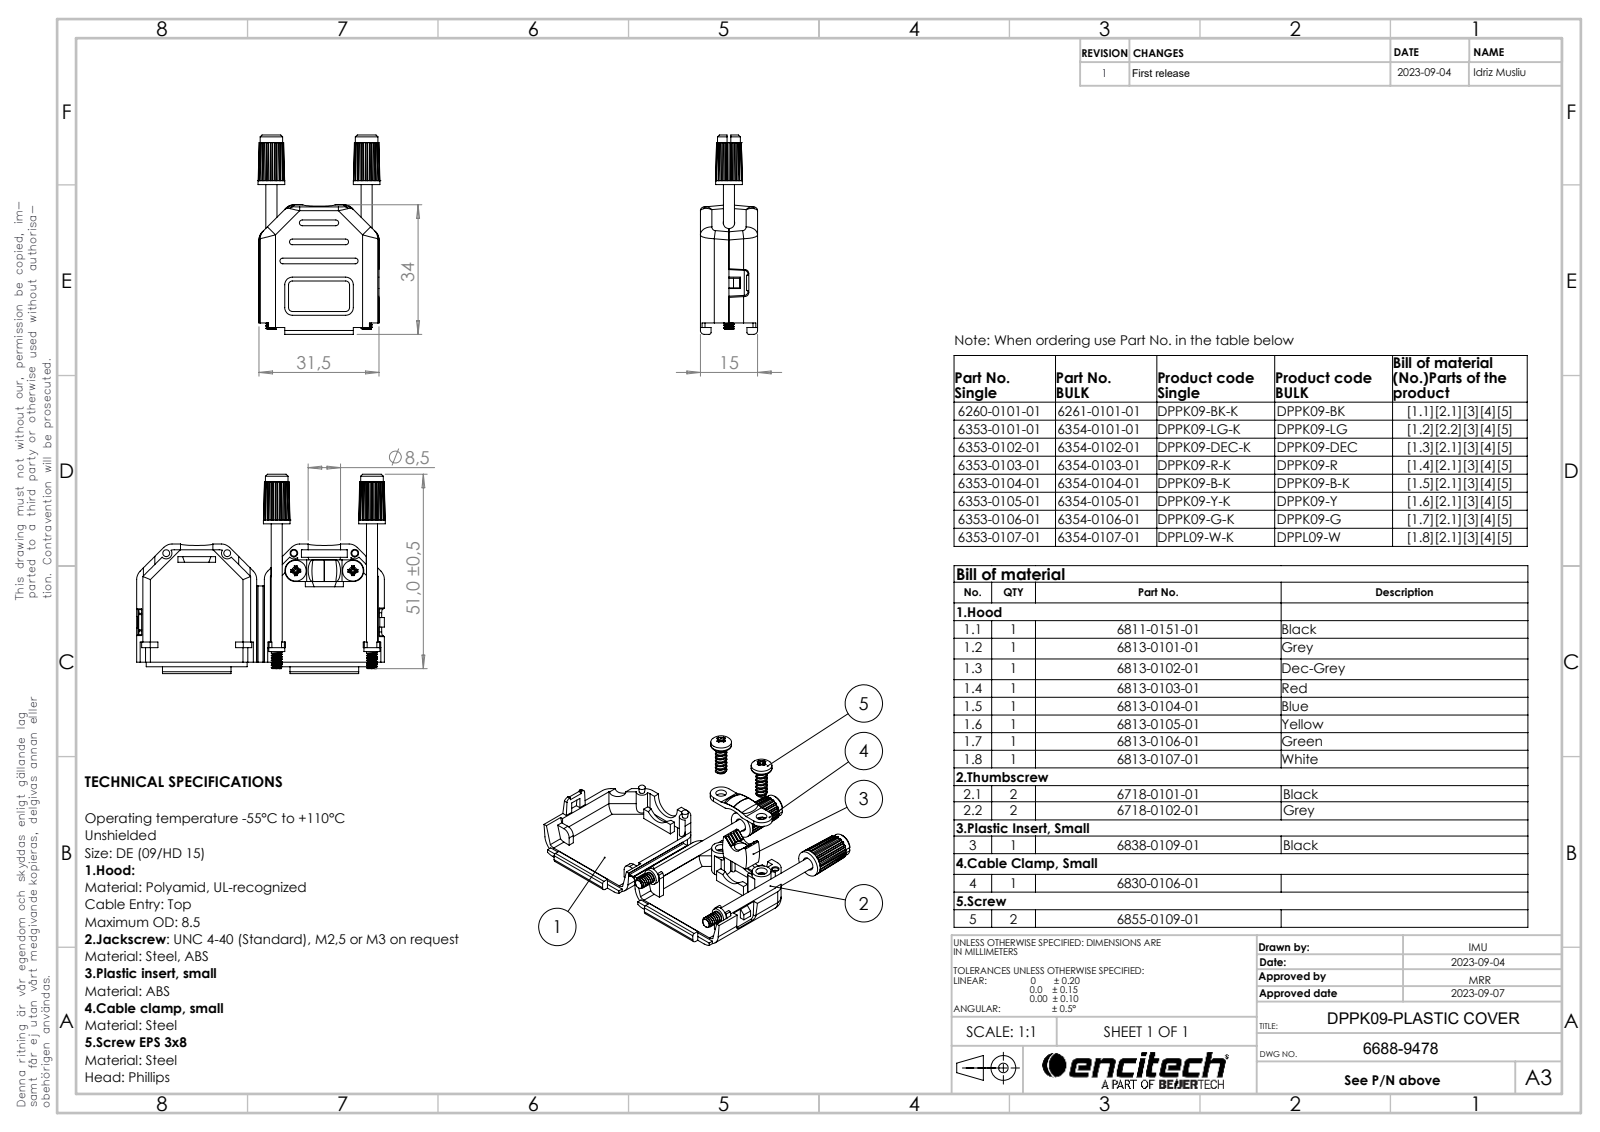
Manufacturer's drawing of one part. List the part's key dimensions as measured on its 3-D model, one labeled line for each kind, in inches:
Part name (STEP PRODUCT): 6830-0106-01; 6718-0101-01; 6811-0151-01 Part 1; 6855-0109-01 (+3 more)
STEP written by: SolidWorks 2023 (AUTOMOTIVE_DESIGN)
Units: inches
Bodies: 10 solids, 839 faces (481 planar, 240 cylindrical, 118 other)
Overall size (bounding box): 2.059 × 1.26 × 0.591
Volume: 0.392 in³ · Surface area: 14.48 in²
Round holes (diameter × count): ⌀0.118 ×4, ⌀0.063 ×2, ⌀0.079 ×2, ⌀0.094 ×2, ⌀0.11 ×2, ⌀0.138 ×1, ⌀0.335 ×1
Round bosses / shafts (diameter × count): ⌀0.276 ×2, ⌀0.236 ×2, ⌀0.215 ×2, ⌀0.197 ×2, ⌀0.165 ×2, ⌀0.114 ×2, ⌀0.112 ×2, ⌀0.097 ×2
Partial cylindrical surfaces — rounded edges, fillets, slot ends (radius × count): R0.079 ×15, R0.118 ×14, R0.039 ×12, R0.02 ×10, R0.03 ×6, R0.016 ×4, R0.157 ×4, R0.059 ×2
Main face-to-face distances: 0.067, 0.524, 0.457, 0.591, 0.228, 0.295, 0.063, 0.059, 0.583, 0.047
Hole centre spacings: 0.182, 0.295, 0.365, 0.492, 0.637, 0.591, 0.63, 0.984
